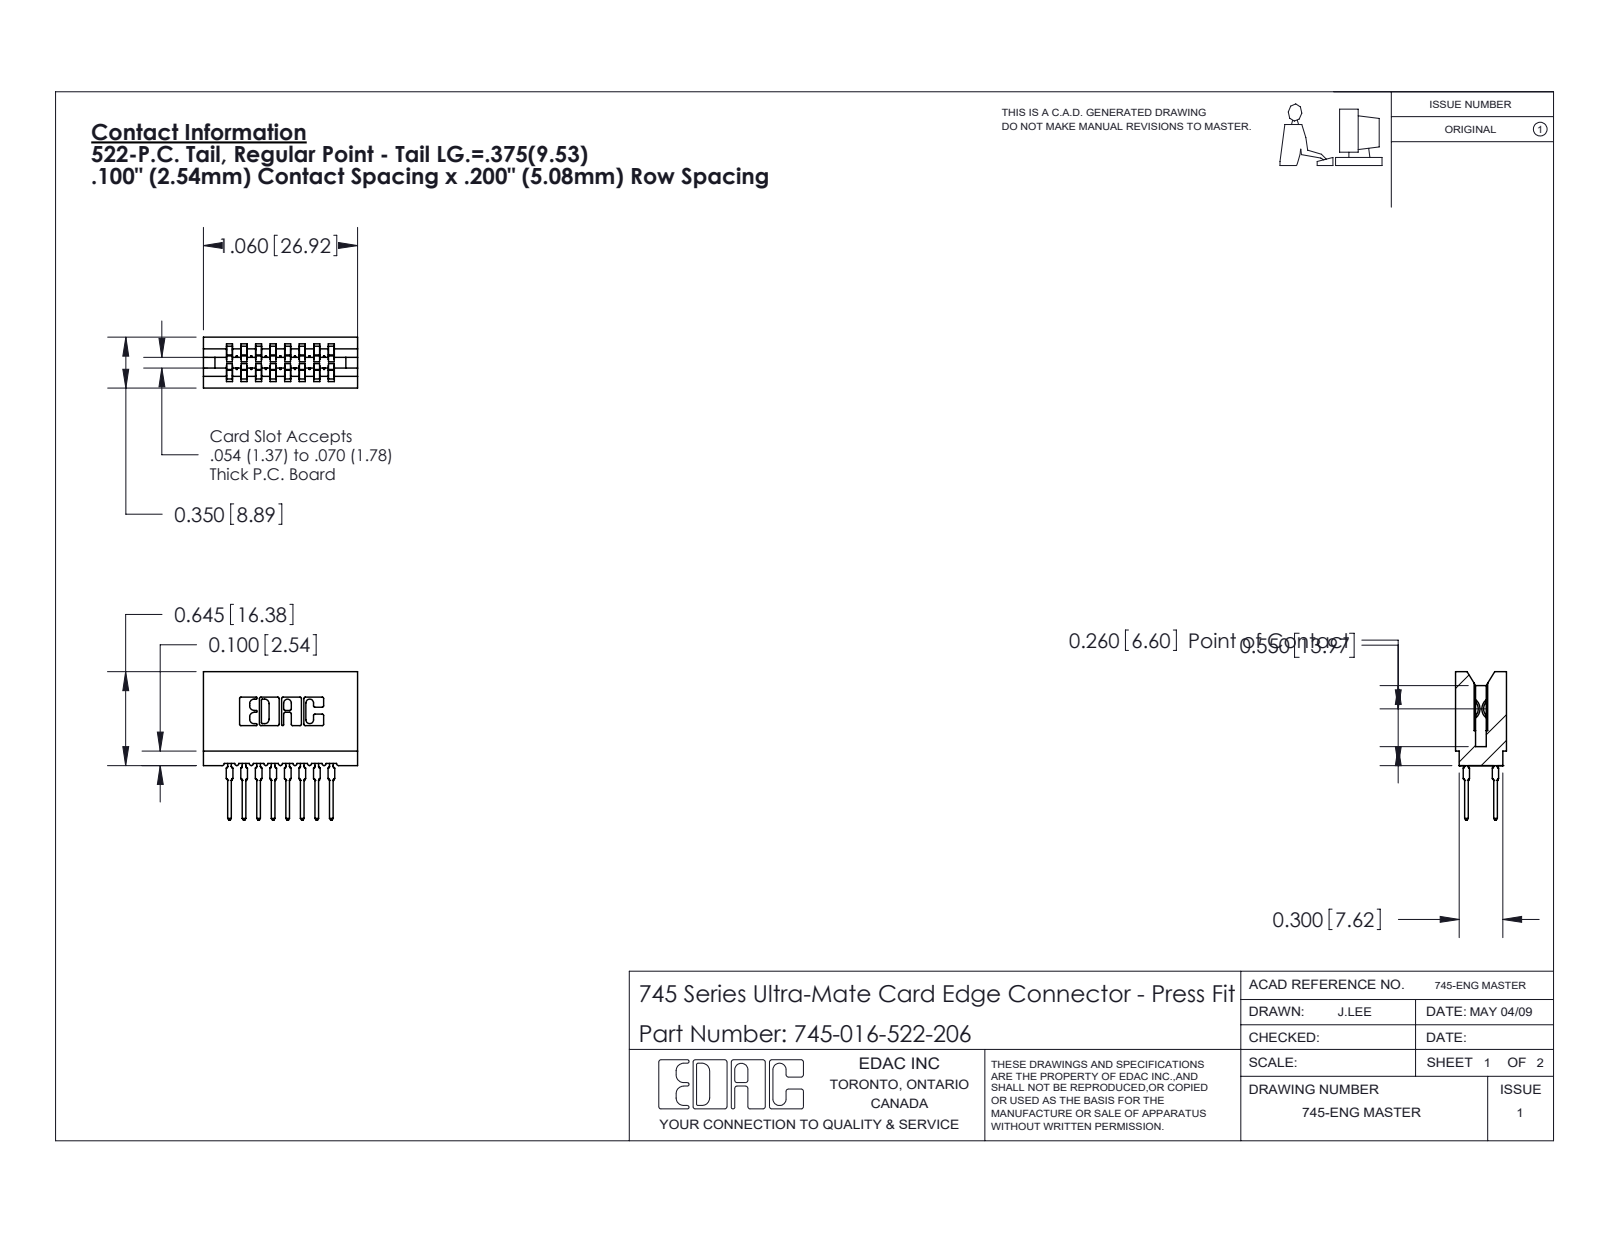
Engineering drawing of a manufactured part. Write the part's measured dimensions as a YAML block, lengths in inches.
part_name: "745-292-001_522; 745 Part_Insulator Option - 06; 745-016-522-206"
step_written_by: "SolidWorks 2020 (CONFIG_CONTROL_DESIGN)"
units: inches
bodies: {solids: 17, faces: 1528, planar: 792, cylindrical: 320, other: 416}
overall_size: [1.06, 1.021, 0.35]
volume: 0.16
surface_area: 7.178
partial_cylinders:
  - {radius: 0.021, count: 32}
  - {radius: 0.01, count: 22}
  - {radius: 0.015, count: 16}
  - {radius: 0.005, count: 8}
  - {radius: 0.011, count: 8}
  - {radius: 0.007, count: 6}
  - {radius: 0.031, count: 6}
  - {radius: 0.026, count: 3}
face_to_face_distances: [0.1, 0.2, 0.3, 0.042, 0.4, 0.142, 0.058, 0.242, 0.5, 0.158]
